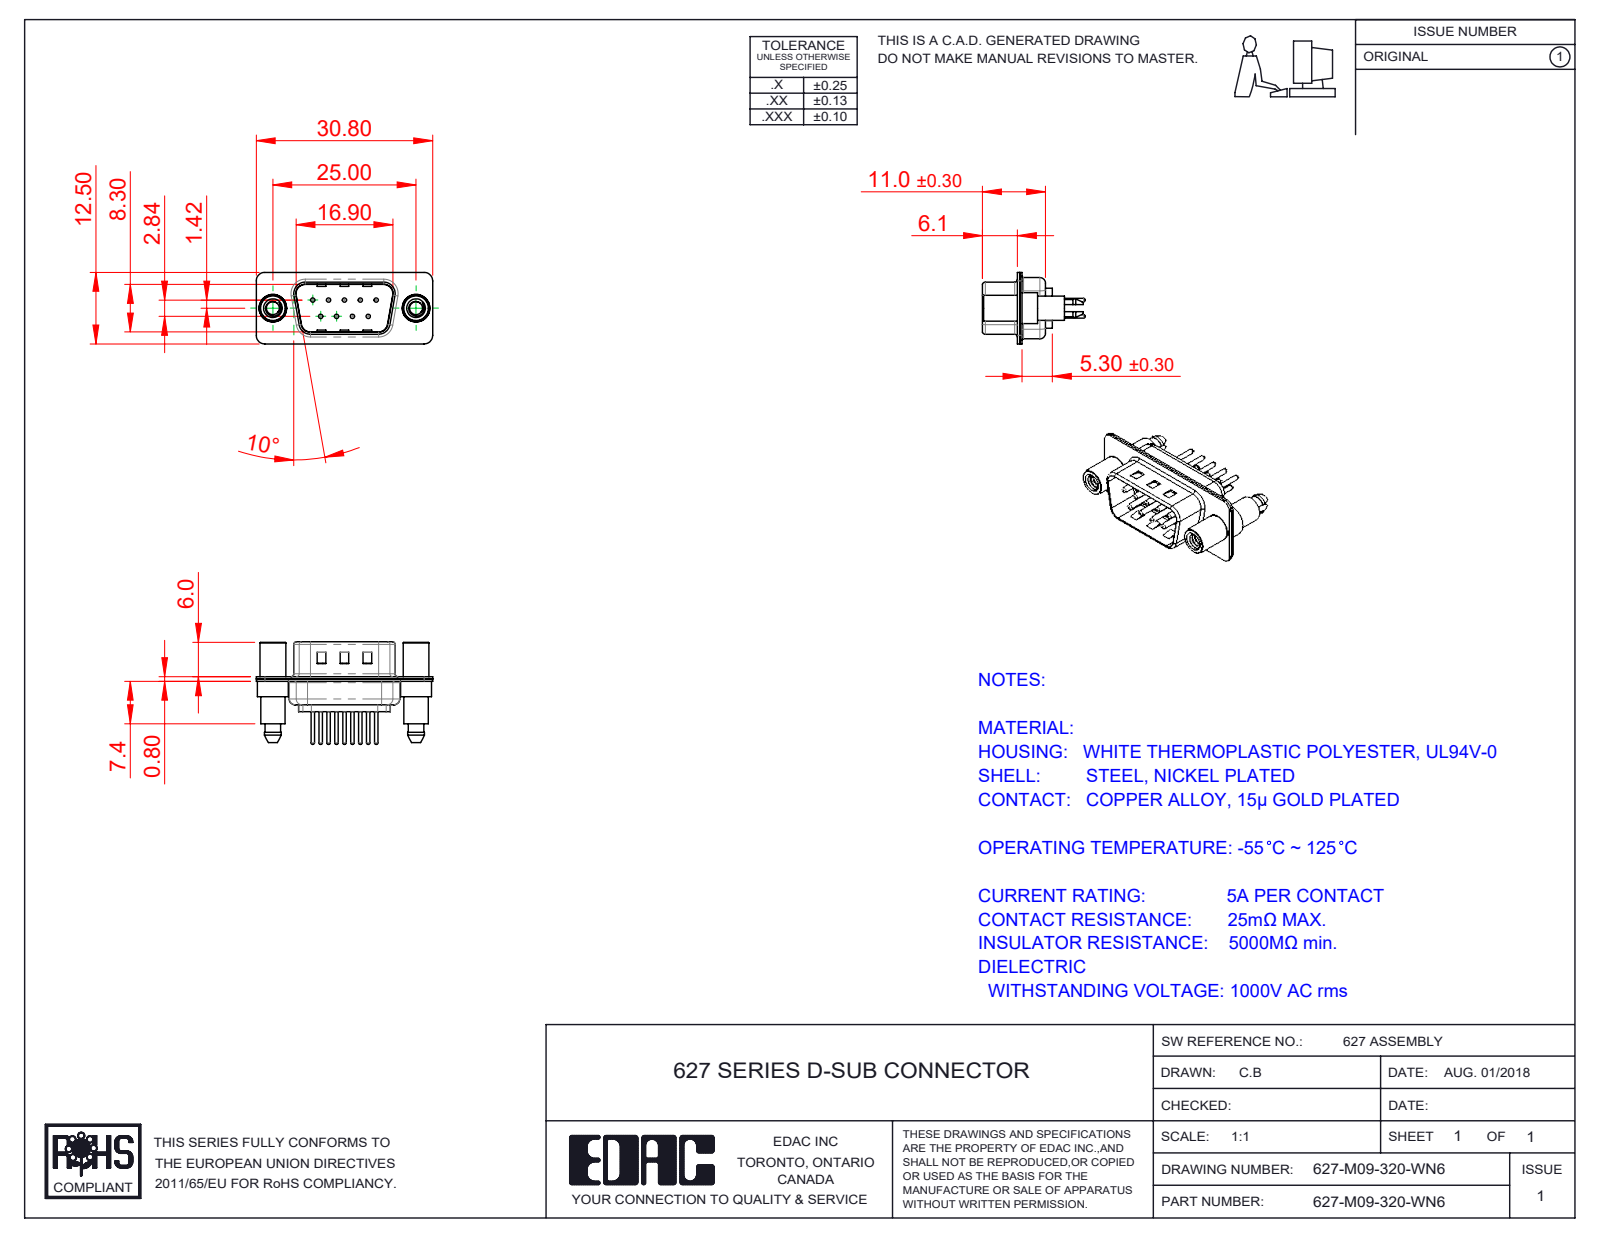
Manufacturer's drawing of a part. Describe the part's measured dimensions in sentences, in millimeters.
The part is named "627M 4-40 Threaded Standoff and Boardlock; 627M Shell Front_09 Contacts; 627M Shell Rear_09 Contacts; 627-M09-320-WN6 (+3 more)". Its 3-D file was written by "SolidWorks 2020 (CONFIG_CONTROL_DESIGN)". It is 14 solids with 689 faces: 188 planar, 283 cylindrical and 218 other. Overall it measures 30.8 by 17.9 by 12.5 millimeters. Its volume is 1 649 cubic millimeters and its surface area 4 042 square millimeters. Round holes: 9 of diameter 0.75, 9 of diameter 1.6, 9 of diameter 2, 2 of diameter 2.26, 2 of diameter 4, 2 of diameter 4.8. Round bosses or shafts: 9 of diameter 1.5, 9 of diameter 0.6, 2 of diameter 5.4, 2 of diameter 4.9, 2 of diameter 4.5, 2 of diameter 4.25. Partial cylindrical surfaces (rounded edges, fillets, slot ends): 18 of radius 1.5, 12 of radius 2, 10 of radius 1.6, 8 of radius 0.5, 4 of radius 0.25, 4 of radius 0.6, 4 of radius 0.65, 4 of radius 0.9. The main face-to-face distances are 0.4, 0.8, 9.5, 9.1, 8.7, 0.65, 9.9, 1.2, 5.3, 6.1. The hole center spacings are 3.16, 2.77, 5.54, 5.03, 5.04, 8.31, 7.1, 7.48.
